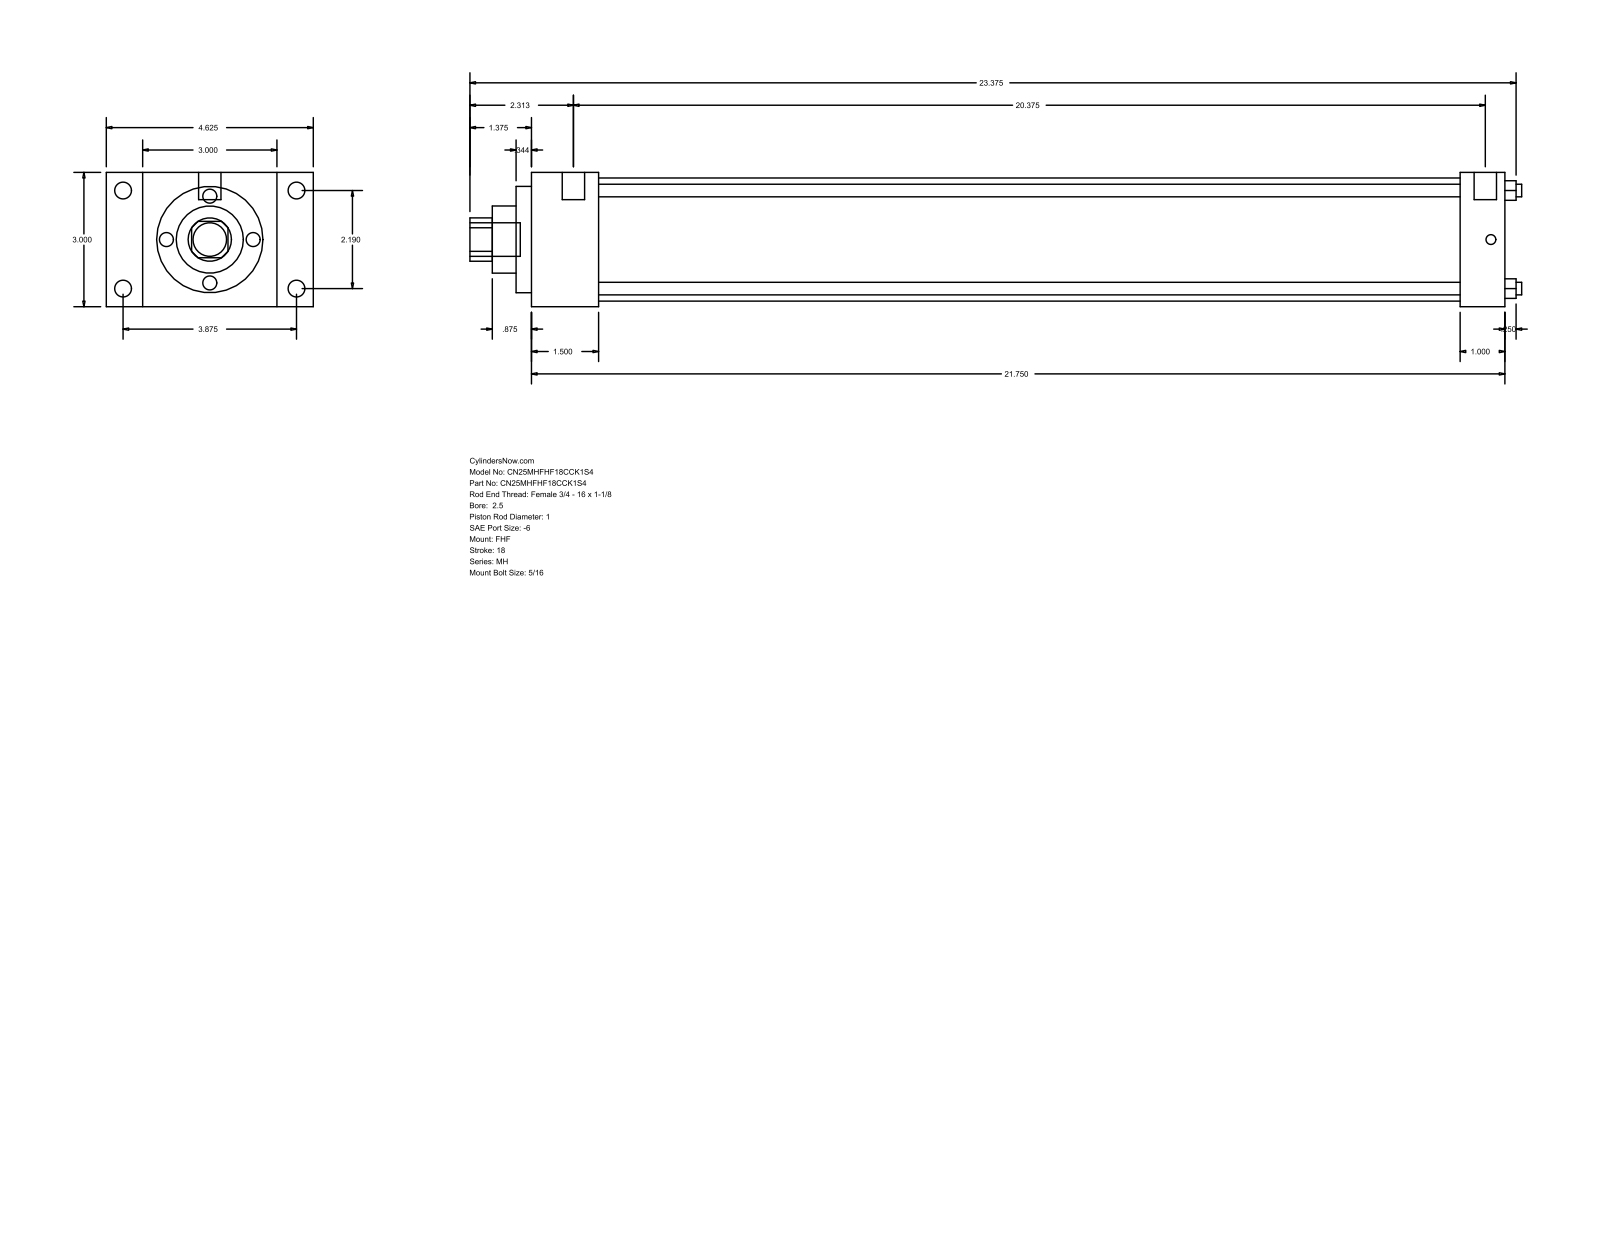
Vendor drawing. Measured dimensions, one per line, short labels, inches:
name: MH_FHF__0250_1
written by: GSSL Pune (CONFIG_CONTROL_DESIGN)
unit: in
bodies: 0 solids, 90 faces (61 planar, 29 cylindrical, 0 other)
size: 23.5 × 4.625 × 3
holes: 4× ⌀0.281, 1× ⌀1, 1× ⌀1.5, 1× ⌀2.375, 1× ⌀2.75
bosses: 4× ⌀0.375, 4× ⌀0.219, 2× ⌀0.5, 1× ⌀0.75
rounds: 1× R0.484
face distances: 3, 21.75, 1.5, 20.25, 0.813, 3.813, 4.625, 20.75, 19.25, 1
hole spacings: 1.548, 2.19, 3.097
